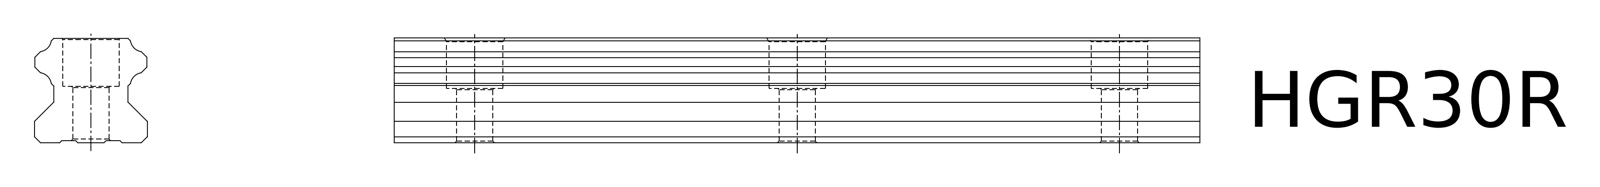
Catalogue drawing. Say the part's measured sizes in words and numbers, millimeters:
The part is named "HGR30R". Its 3-D file was written by "SolidWorks 2006104 (CONFIG_CONTROL_DESIGN)". It is 1 solid with 67 faces: 33 planar, 34 cylindrical and 0 other. Overall it measures 200 by 28 by 26 millimeters. Its volume is 114 437 cubic millimeters and its surface area 25 670 square millimeters. Round holes: 3 of diameter 9, 3 of diameter 14. Partial cylindrical surfaces (rounded edges, fillets, slot ends): 12 of radius 0.6, 6 of radius 0.8, 4 of radius 2.83. The main face-to-face distances are 26, 4.7, 23.3, 28, 11.18, 33.76, 22.58, 21.57, 10.39, 12.19. The hole center spacings are 80, 160.
